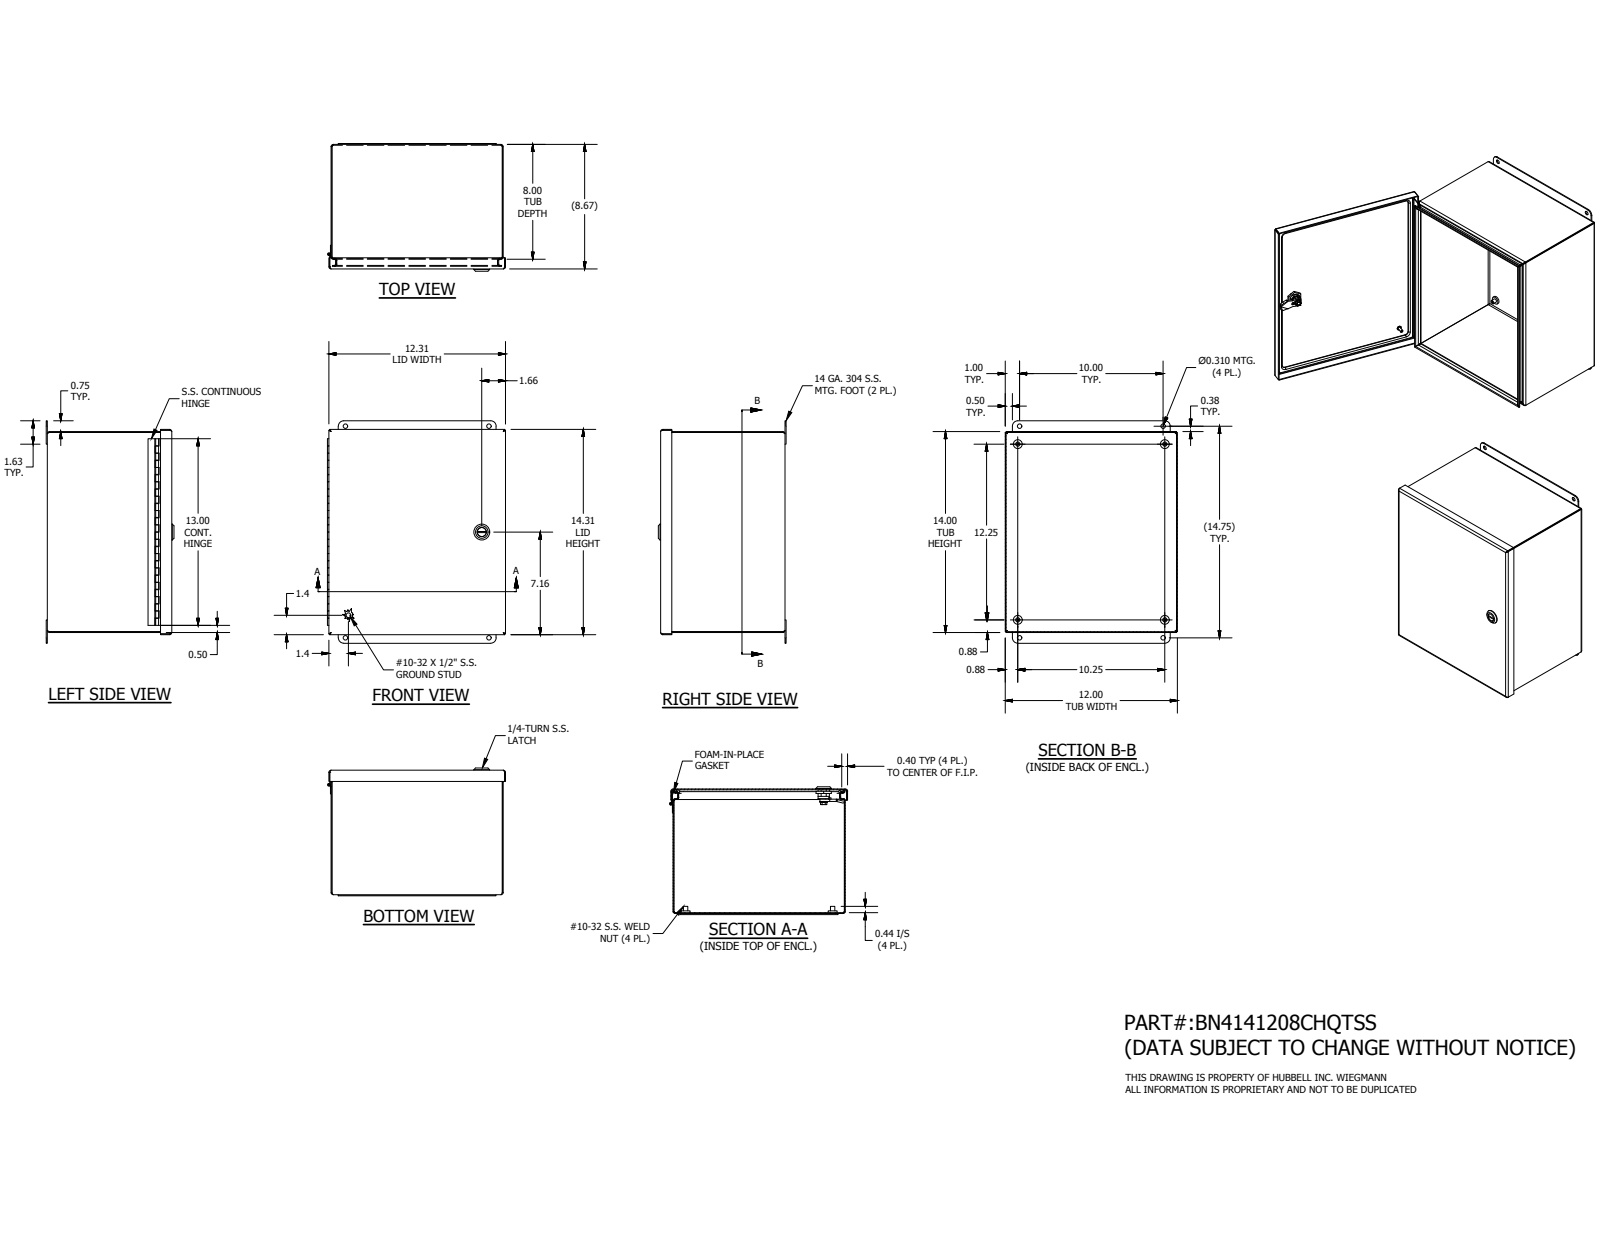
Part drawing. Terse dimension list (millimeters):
name: BN41412CHQTSSLID; 14x12; 34856; H4050553LH (+8 more)
written by: Autodesk Inventor 2016 (AUTOMOTIVE_DESIGN)
unit: mm
bodies: 19 solids, 648 faces (347 planar, 207 cylindrical, 94 other)
size: 393.7 × 315.26 × 226.19
volume: 951 107 mm³; area: 1 206 000 mm²
holes: 4× ⌀3.96, 4× ⌀7.87, 1× ⌀2.96, 1× ⌀5, 1× ⌀8, 1× ⌀10, 1× ⌀10.2, 1× ⌀16.1
bosses: 4× ⌀15.88, 4× ⌀7.62, 1× ⌀28, 1× ⌀19.8, 1× ⌀16, 1× ⌀15.2, 1× ⌀13.5, 1× ⌀12.8
rounds: 20× R2.38, 20× R3.88, 16× R3.17, 8× R0.5, 4× R4, 4× R9.53, 2× R2.31, 1× R6.45
face distances: 1.5, 1.49, 354.1, 218.79, 220.28, 217.29, 218.78, 304.8, 303.3, 303.31
hole spacings: 31.91, 342.91, 254, 259.12, 259.13, 260.35, 305.47, 311.15
